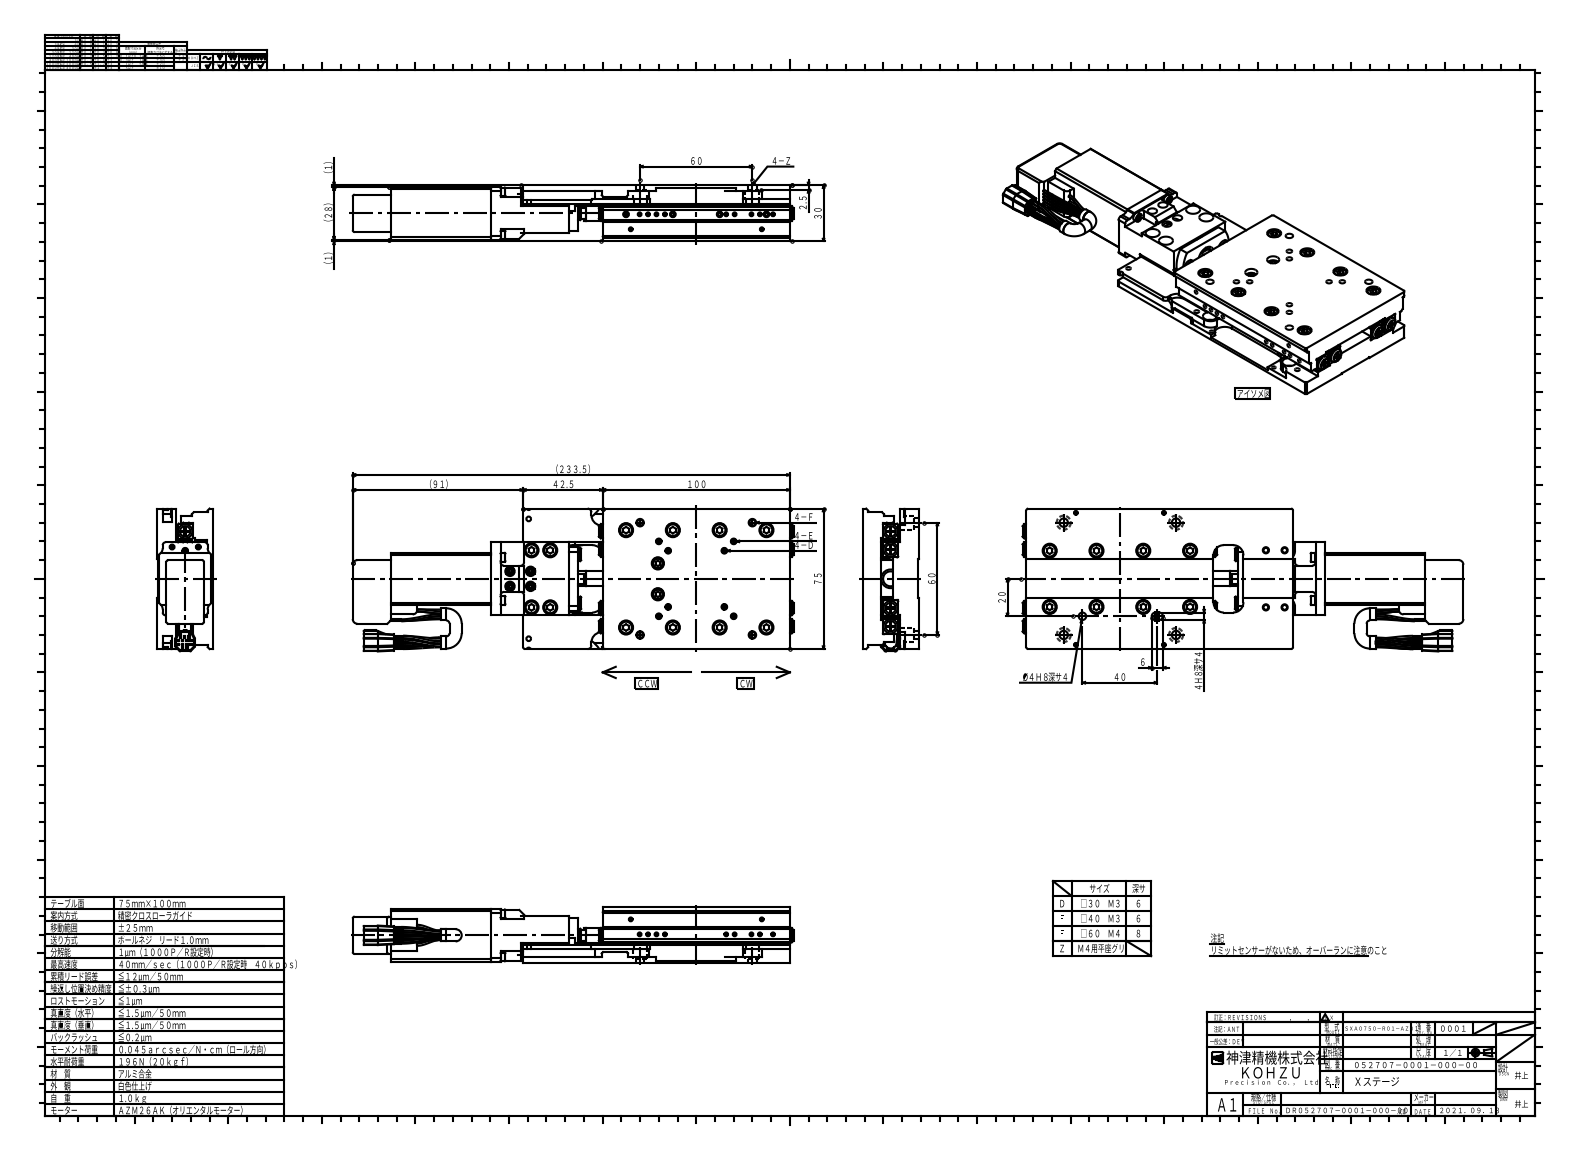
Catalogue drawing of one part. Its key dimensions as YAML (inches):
part_name: "SXA0750-R01-AZ01-prt0; SXA0750-R01-AZ01-prt1; SXA0750-R01-AZ01-prt2"
step_written_by: "spGate 17.5.5 (AUTOMOTIVE_DESIGN)"
units: inches
bodies: {solids: 3, faces: 999, planar: 520, cylindrical: 327, other: 152}
overall_size: [9.272, 3.003, 1.181]
volume: 18.21
surface_area: 113.3
round_holes:
  - {diameter: 0.079, count: 15}
  - {diameter: 0.098, count: 10}
  - {diameter: 0.118, count: 10}
  - {diameter: 0.085, count: 8}
  - {diameter: 0.102, count: 8}
  - {diameter: 0.157, count: 5}
  - {diameter: 0.13, count: 4}
  - {diameter: 0.177, count: 4}
  - {diameter: 0.295, count: 4}
  - {diameter: 0.063, count: 2}
  - {diameter: 0.236, count: 2}
round_bosses_or_shafts:
  - {diameter: 0.038, count: 10}
  - {diameter: 0.299, count: 4}
  - {diameter: 0.197, count: 4}
  - {diameter: 0.177, count: 4}
  - {diameter: 0.048, count: 4}
  - {diameter: 0.256, count: 3}
  - {diameter: 0.276, count: 2}
  - {diameter: 0.217, count: 2}
partial_cylinders:
  - {radius: 0.039, count: 18}
  - {radius: 0.217, count: 18}
  - {radius: 0.02, count: 12}
  - {radius: 0.024, count: 4}
  - {radius: 0.059, count: 4}
  - {radius: 0.071, count: 4}
  - {radius: 0.157, count: 4}
  - {radius: 0.197, count: 4}
face_to_face_distances: [0.394, 0.748, 0.039, 0.354, 1.181, 0.787, 0.433, 0.709, 0.079, 0.382]
hole_center_spacings: [1.392, 1.867, 2.007, 0.177, 1.181, 0.278, 0.287, 0.325]
